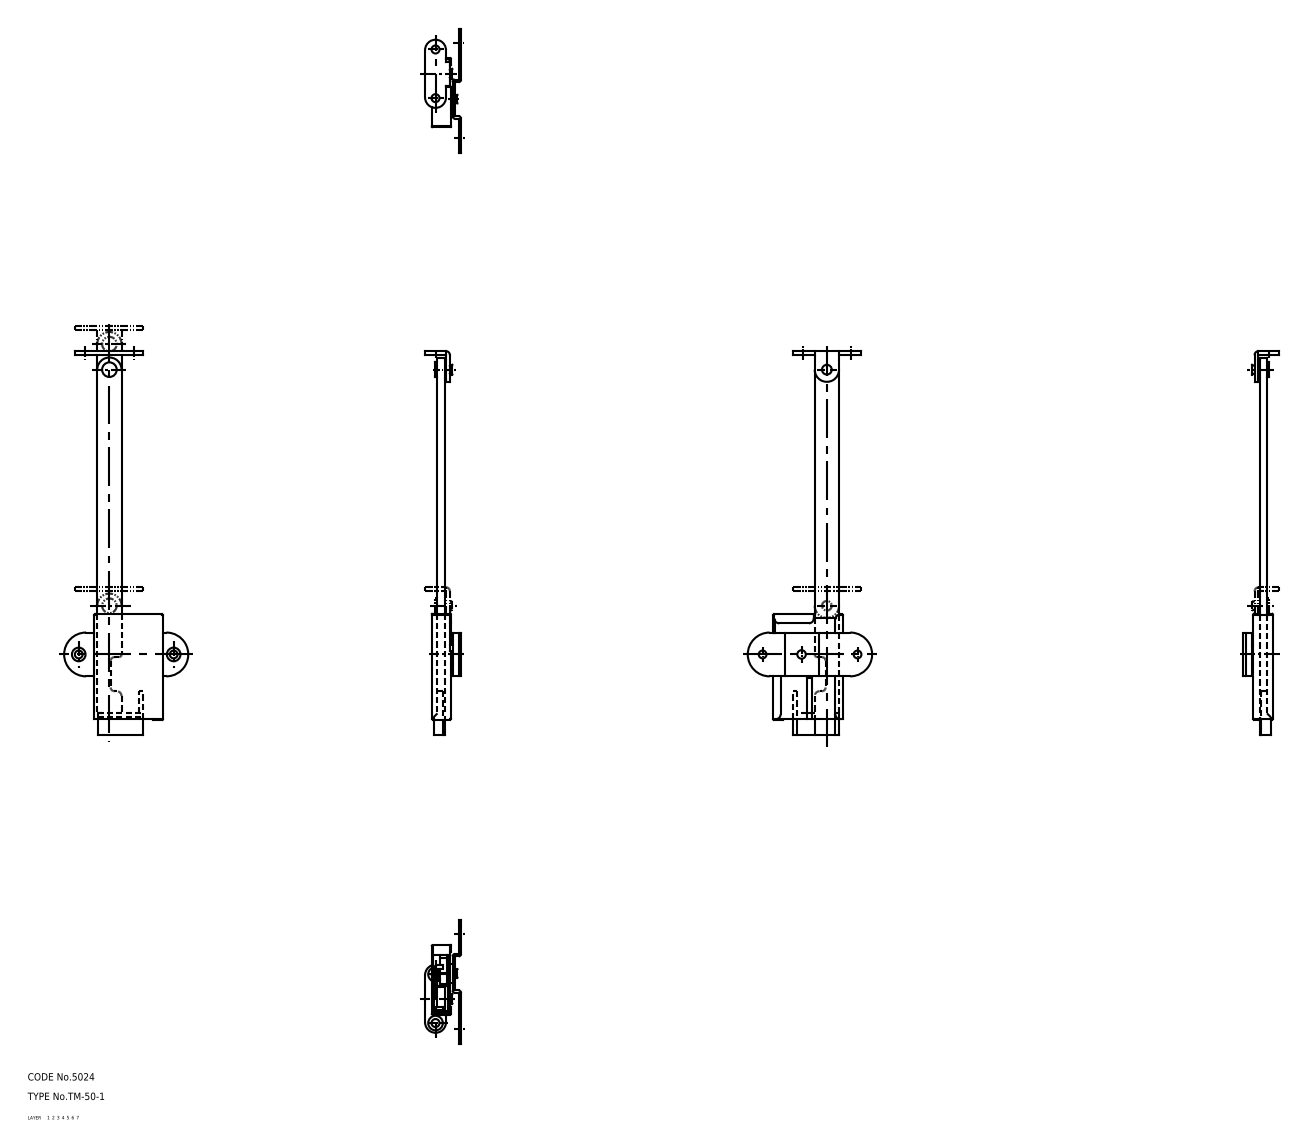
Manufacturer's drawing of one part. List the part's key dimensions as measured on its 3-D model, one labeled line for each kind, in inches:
Part name (STEP PRODUCT): bracket_B; bracket_A; rivet_A; washer_B (+8 more)
STEP written by: CADfix (AUTOMOTIVE_DESIGN)
Units: inches
Bodies: 14 solids, 204 faces (0 planar, 0 cylindrical, 204 other)
Overall size (bounding box): 6.205 × 2.008 × 0.583
Volume: 0.611 in³ · Surface area: 28.58 in²
